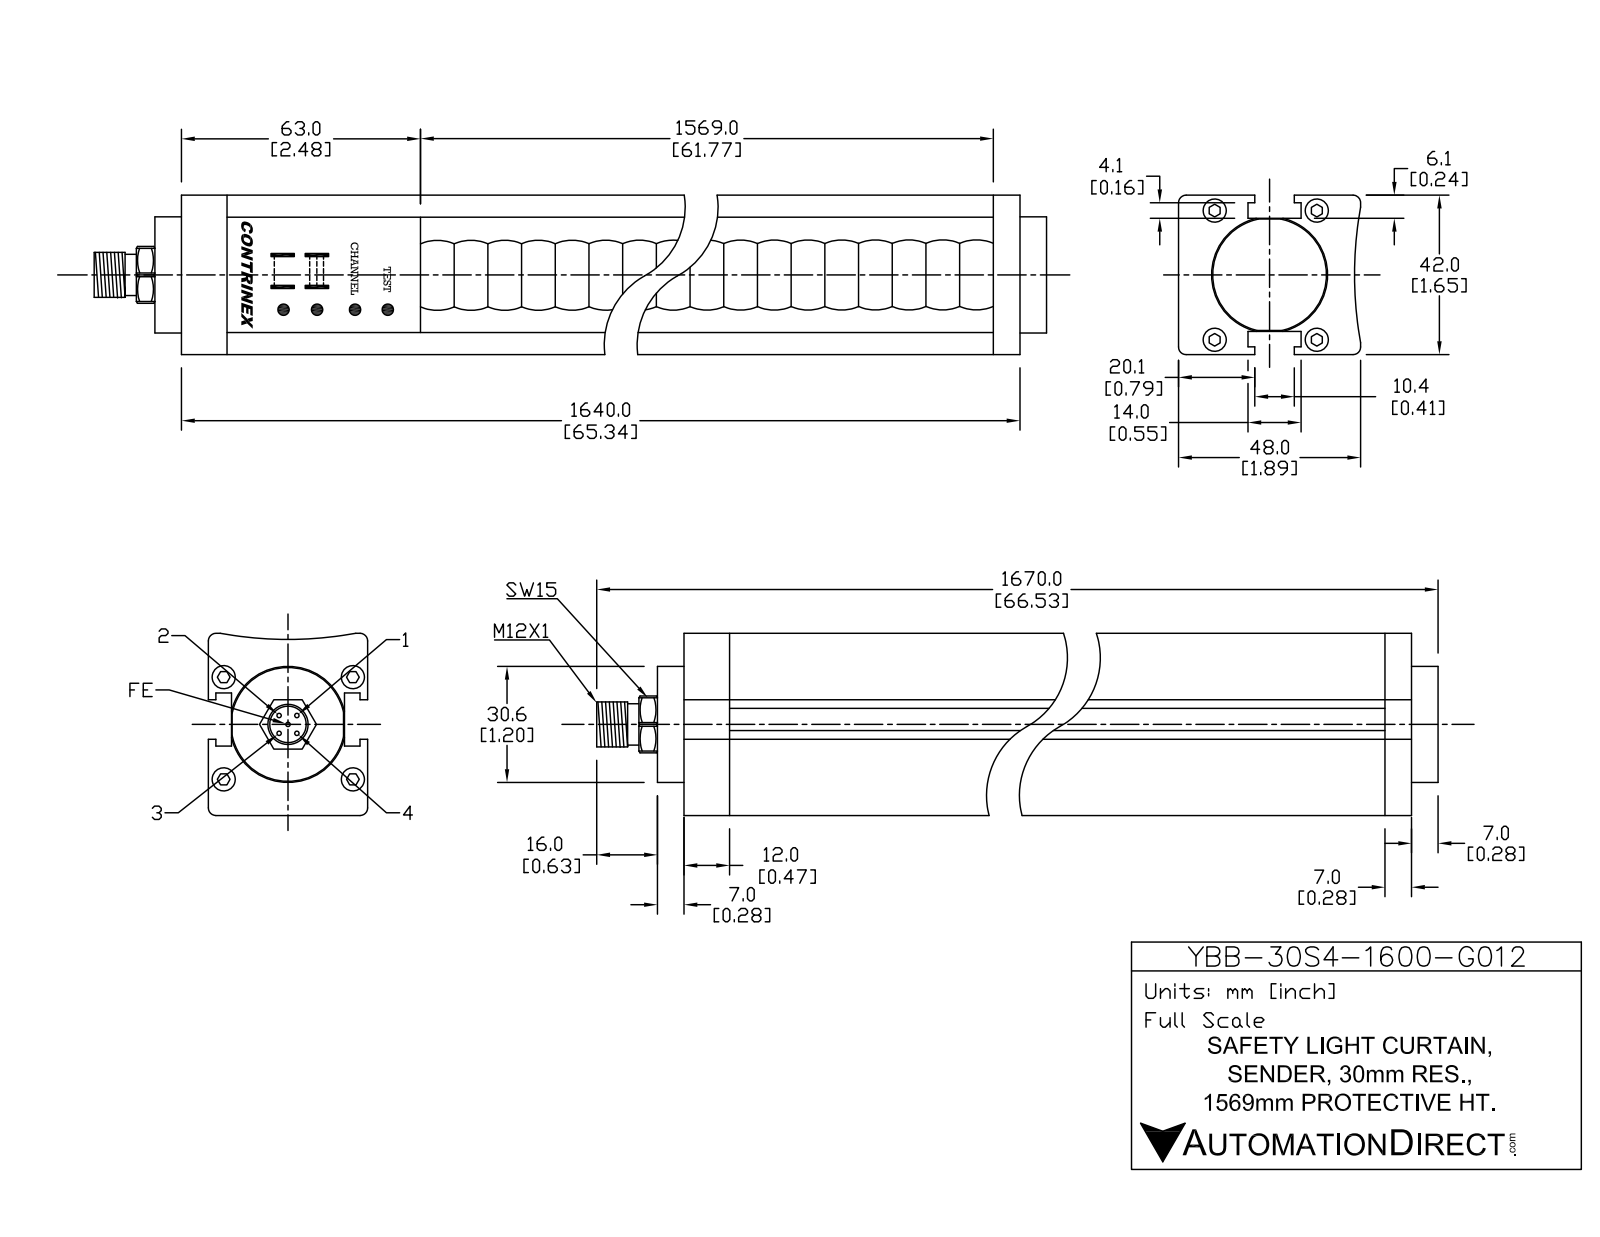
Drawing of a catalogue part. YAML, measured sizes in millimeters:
part_name: "YBB-30S4-1600-G012"
step_written_by: "SolidWorks 2016 (AUTOMOTIVE_DESIGN)"
units: millimeters
bodies: {solids: 19, faces: 440, planar: 208, cylindrical: 168, other: 64}
overall_size: [1670, 48, 42]
volume: 2946000
surface_area: 367270
round_holes:
  - {diameter: 6, count: 4}
  - {diameter: 8.5, count: 1}
  - {diameter: 32, count: 1}
round_bosses_or_shafts:
  - {diameter: 1, count: 5}
  - {diameter: 5.5, count: 4}
  - {diameter: 30.6, count: 1}
  - {diameter: 12, count: 1}
  - {diameter: 10.5, count: 1}
partial_cylinders:
  - {radius: 1, count: 48}
  - {radius: 0.5, count: 4}
  - {radius: 0.55, count: 2}
  - {radius: 8.2, count: 1}
  - {radius: 100, count: 1}
face_to_face_distances: [6.3, 35.7, 42, 29.4, 14, 17.2, 31.2, 15.7, 29.7, 46.9]
hole_center_spacings: [21.04, 22.34, 26.9, 34, 43.35]
